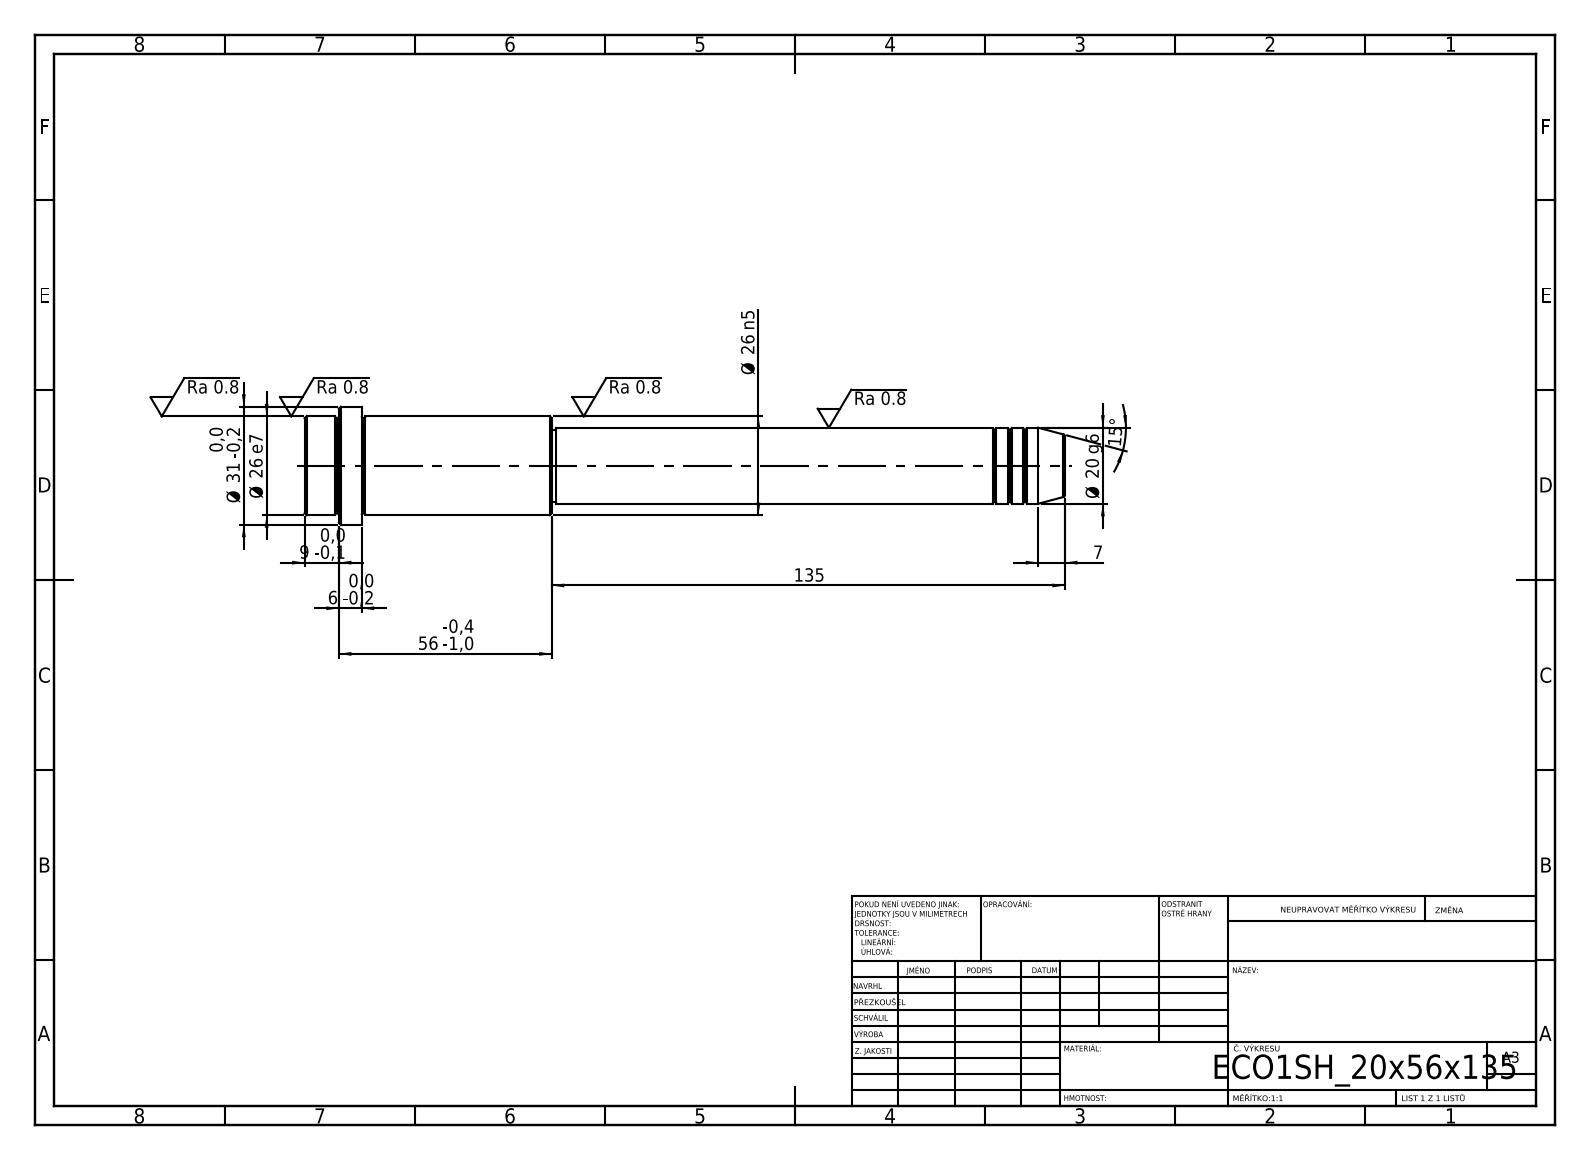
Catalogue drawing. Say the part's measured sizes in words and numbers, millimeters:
Its 3-D file was written by "SolidWorks 2019 (CONFIG_CONTROL_DESIGN)". It is 1 solid with 52 faces: 6 planar, 16 cylindrical and 30 other. Overall it measures 200 by 31 by 31 millimeters. Its volume is 77 678 cubic millimeters and its surface area 15 421 square millimeters. Round bosses or shafts: 1 of diameter 31, 1 of diameter 26, 1 of diameter 20, 1 of diameter 19. The main face-to-face distances are 15, 50, 65, 135, 185, 200, 191, 56, 6, 9.
